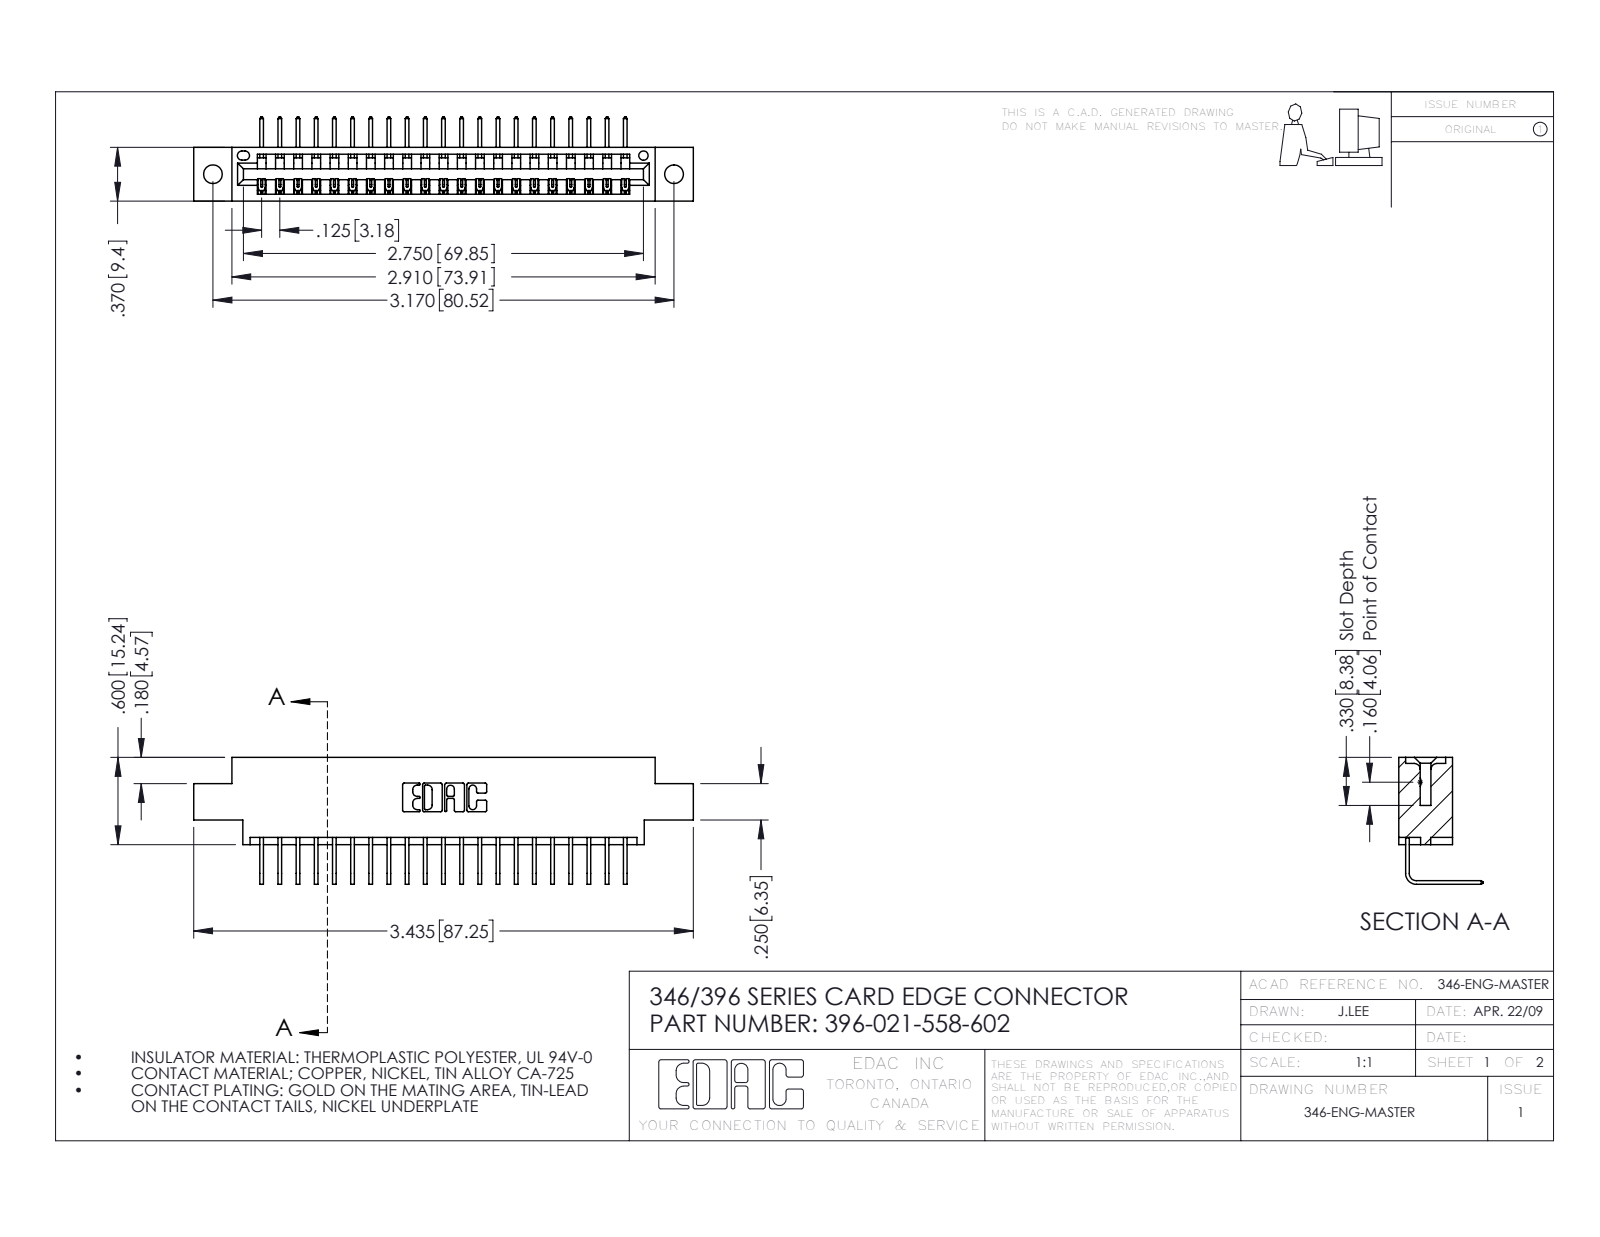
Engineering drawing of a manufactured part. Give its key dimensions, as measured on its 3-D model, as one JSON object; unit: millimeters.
{"part_name": "346 Part_0.170 Offset - 0.128 Dia; 396-021-558-602; 345-292-001_558 Tail - 2", "step_written_by": "SolidWorks 2016 (CONFIG_CONTROL_DESIGN)", "units": "millimeters", "bodies": {"solids": 22, "faces": 1386, "planar": 962, "cylindrical": 424, "other": 0}, "overall_size": [87.2, 22.2, 14.7], "volume_mm3": 8080, "surface_area_mm2": 10190, "round_holes": [[3.3, 2], [1.6, 1]], "partial_cylinders_radius": [[0.2, 42], [0.3, 22], [0.2, 6], [0.8, 6], [0.7, 3], [0.8, 2], [1, 2], [0.4, 1]], "face_to_face_distances": [8.2, 1.2, 9.4, 6.4, 7.6, 0.6, 1.8, 3.8, 5.6, 2.5], "hole_center_spacings": [6.2, 75.3, 80.5]}
